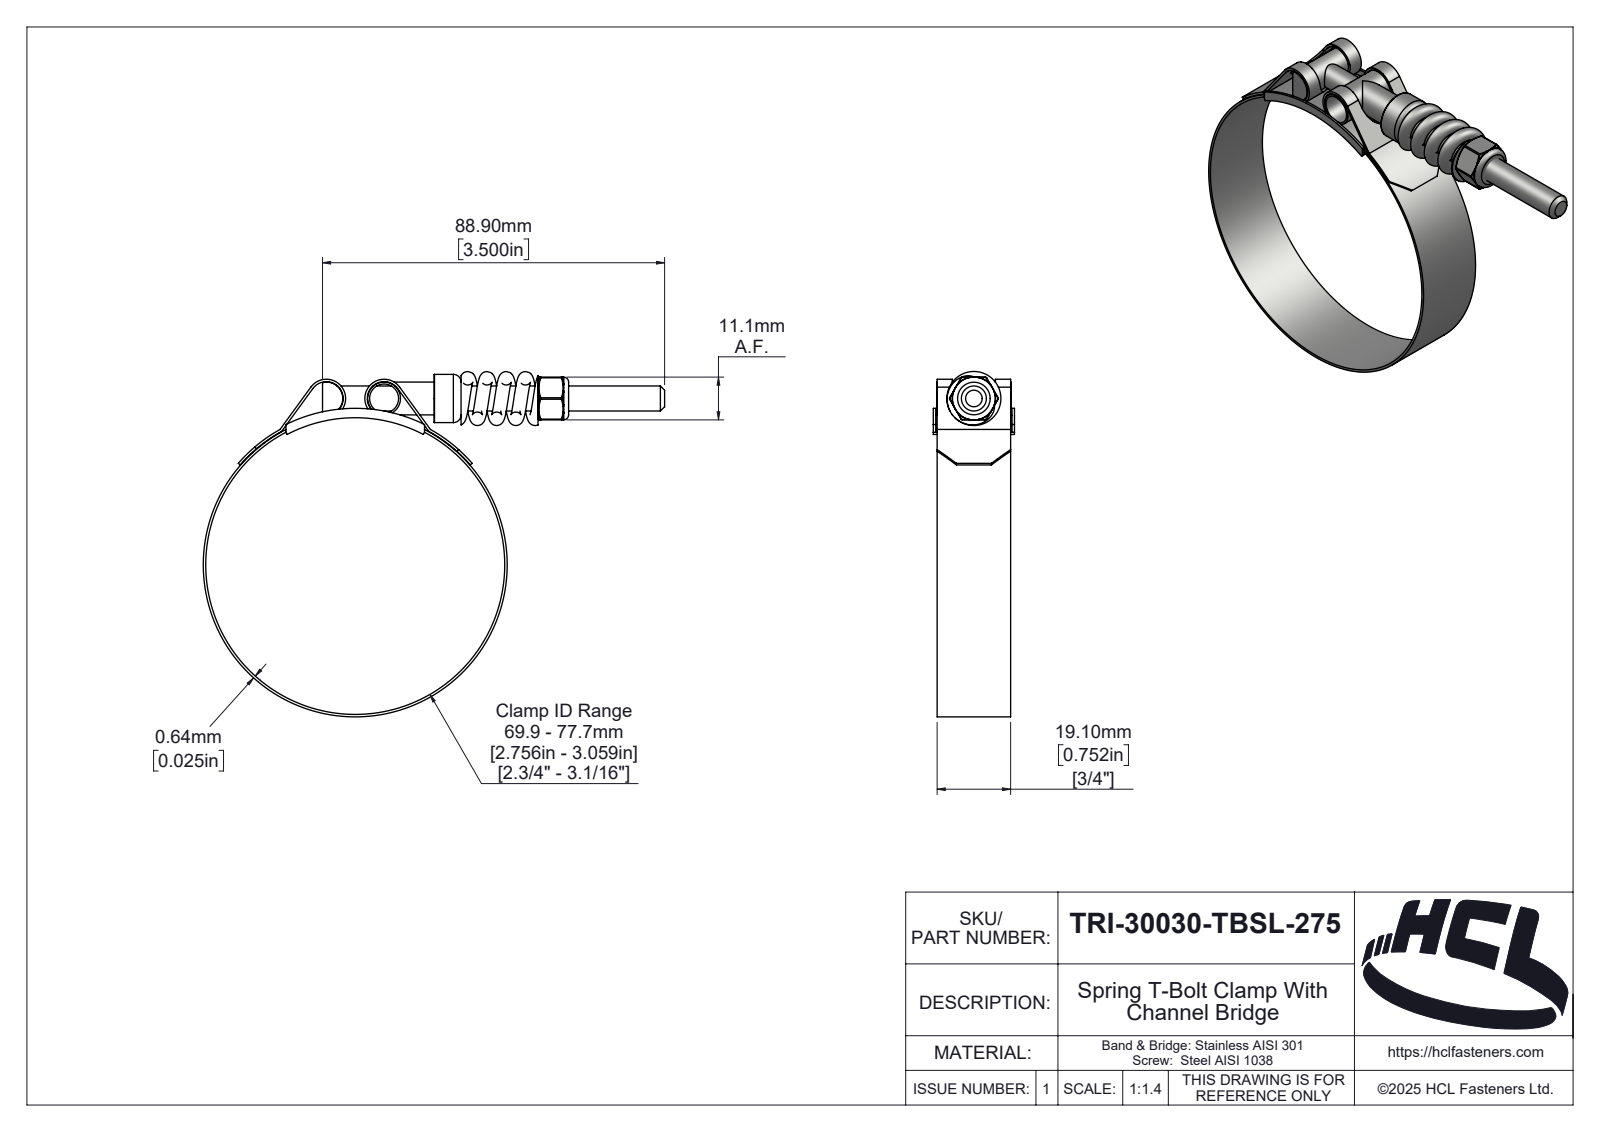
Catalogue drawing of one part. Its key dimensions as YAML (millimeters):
part_name: "TRI-30030-TBSL-275"
step_written_by: "SolidWorks 2025 (AUTOMOTIVE_DESIGN)"
units: millimeters
bodies: {solids: 7, faces: 336, planar: 48, cylindrical: 126, other: 162}
overall_size: [120.89, 89.72, 21.1]
volume: 10642
surface_area: 20305
round_holes:
  - {diameter: 5.4, count: 1}
  - {diameter: 6.35, count: 1}
  - {diameter: 6.5, count: 1}
  - {diameter: 7.52, count: 1}
  - {diameter: 77.7, count: 1}
round_bosses_or_shafts:
  - {diameter: 8.52, count: 2}
  - {diameter: 78.98, count: 1}
  - {diameter: 12.52, count: 1}
partial_cylinders:
  - {radius: 0.39, count: 6}
  - {radius: 0.5, count: 2}
  - {radius: 4.36, count: 2}
  - {radius: 5, count: 2}
  - {radius: 5.6, count: 2}
  - {radius: 0.59, count: 1}
  - {radius: 2.42, count: 1}
  - {radius: 3.03, count: 1}
face_to_face_distances: [0.64, 19.1, 1, 20.1, 20.46, 0.36, 19.46, 56, 11.11, 0.9]
hole_center_spacings: [43.85]
